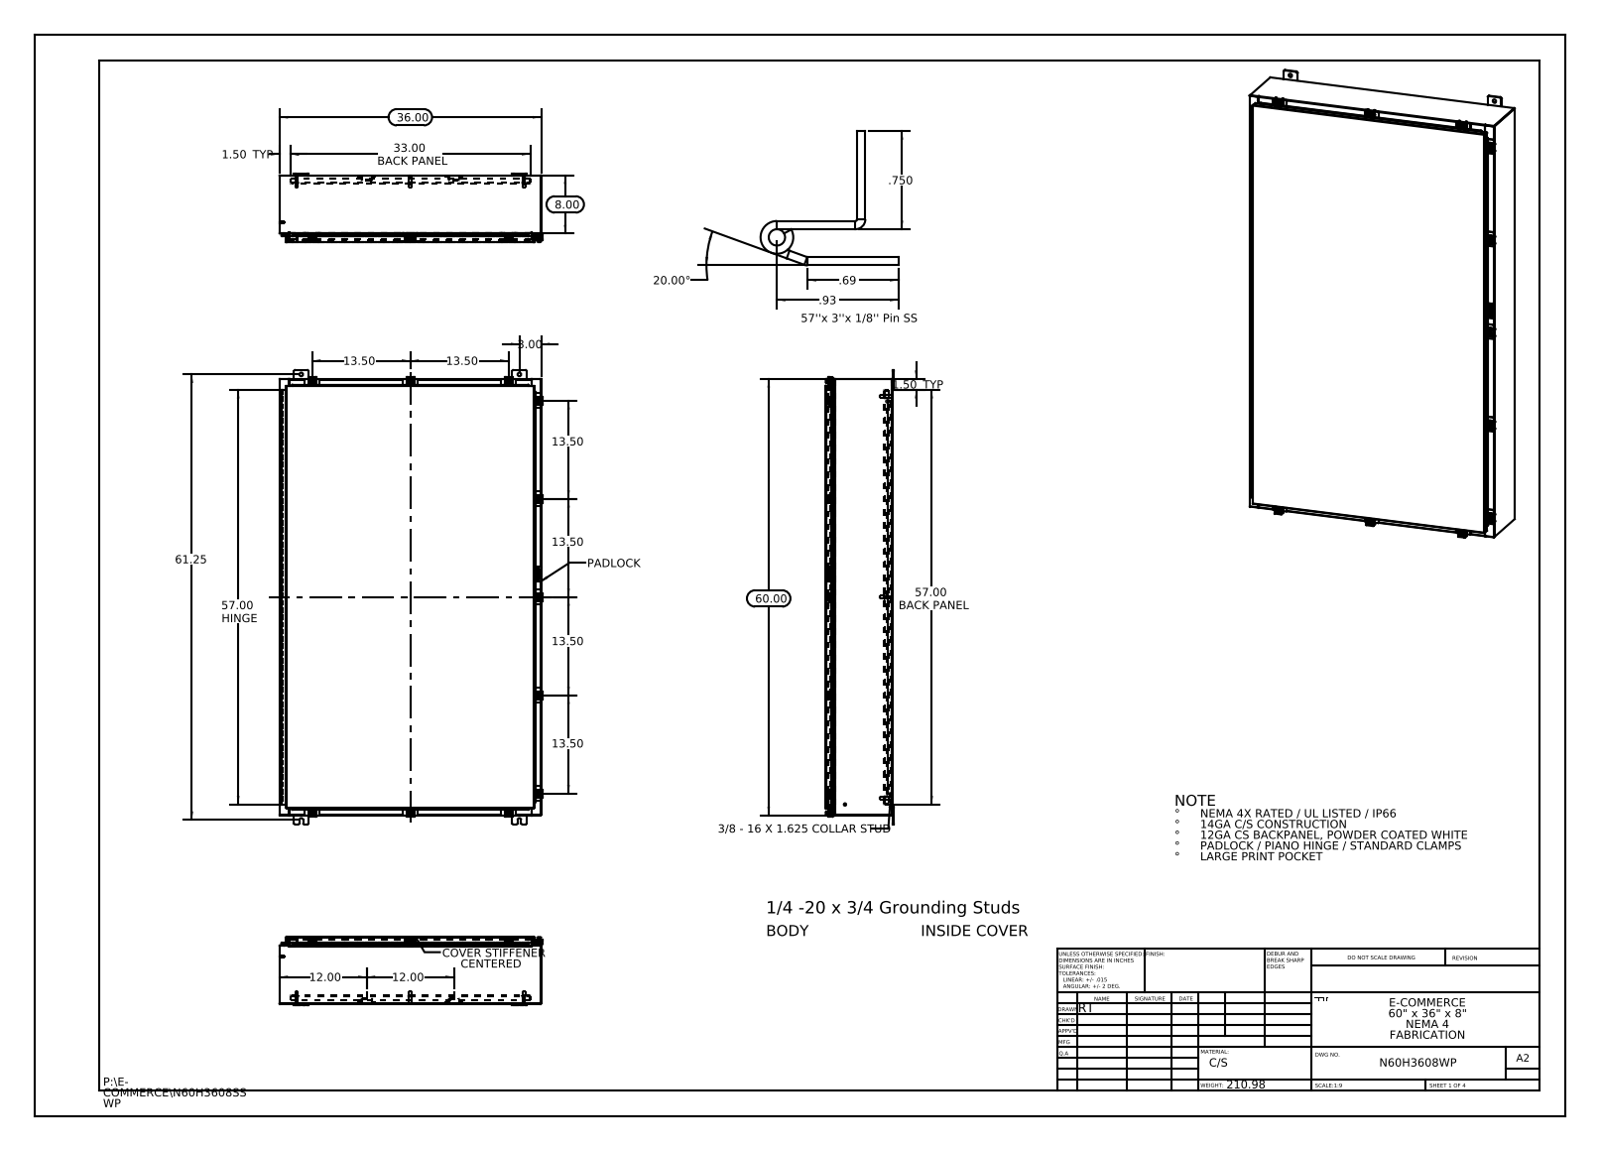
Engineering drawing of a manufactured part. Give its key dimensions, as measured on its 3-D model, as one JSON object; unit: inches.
{"part_name": "N60H3608SSWP Standard Clamps; N60H3608SSWP Hinge Cover Side; N60H3608SSWP Clamp Assembly; N60H3608SSWP Hinge Enclosure Side2 (+8 more)", "step_written_by": "SolidWorks 2013 (CONFIG_CONTROL_DESIGN)", "units": "inches", "bodies": {"solids": 89, "faces": 3554, "planar": 1796, "cylindrical": 1506, "other": 252}, "overall_size": [62.5, 36.211, 9.389], "volume_in3": 738.9, "surface_area_in2": 18321, "round_holes": [[0.5, 12], [0.213, 11], [0.26, 11], [0.25, 8], [0.125, 2]], "round_bosses_or_shafts": [[0.25, 12], [0.5, 11], [0.399, 11], [0.625, 8], [0.375, 8], [0.33, 8], [0.157, 8], [0.14, 8]], "partial_cylinders_radius": [[0.06, 50], [0.013, 39], [0.088, 33], [0.19, 24], [0.12, 22], [0.141, 22], [0.05, 17], [0.08, 16]], "face_to_face_distances": [0.075, 9.126, 9.051, 0.104, 9.201, 1, 8.126, 1.075, 8.051, 1.179], "hole_center_spacings": [13.5, 13.663, 2.225, 27, 27.625, 29.802, 41.709, 57.39]}
